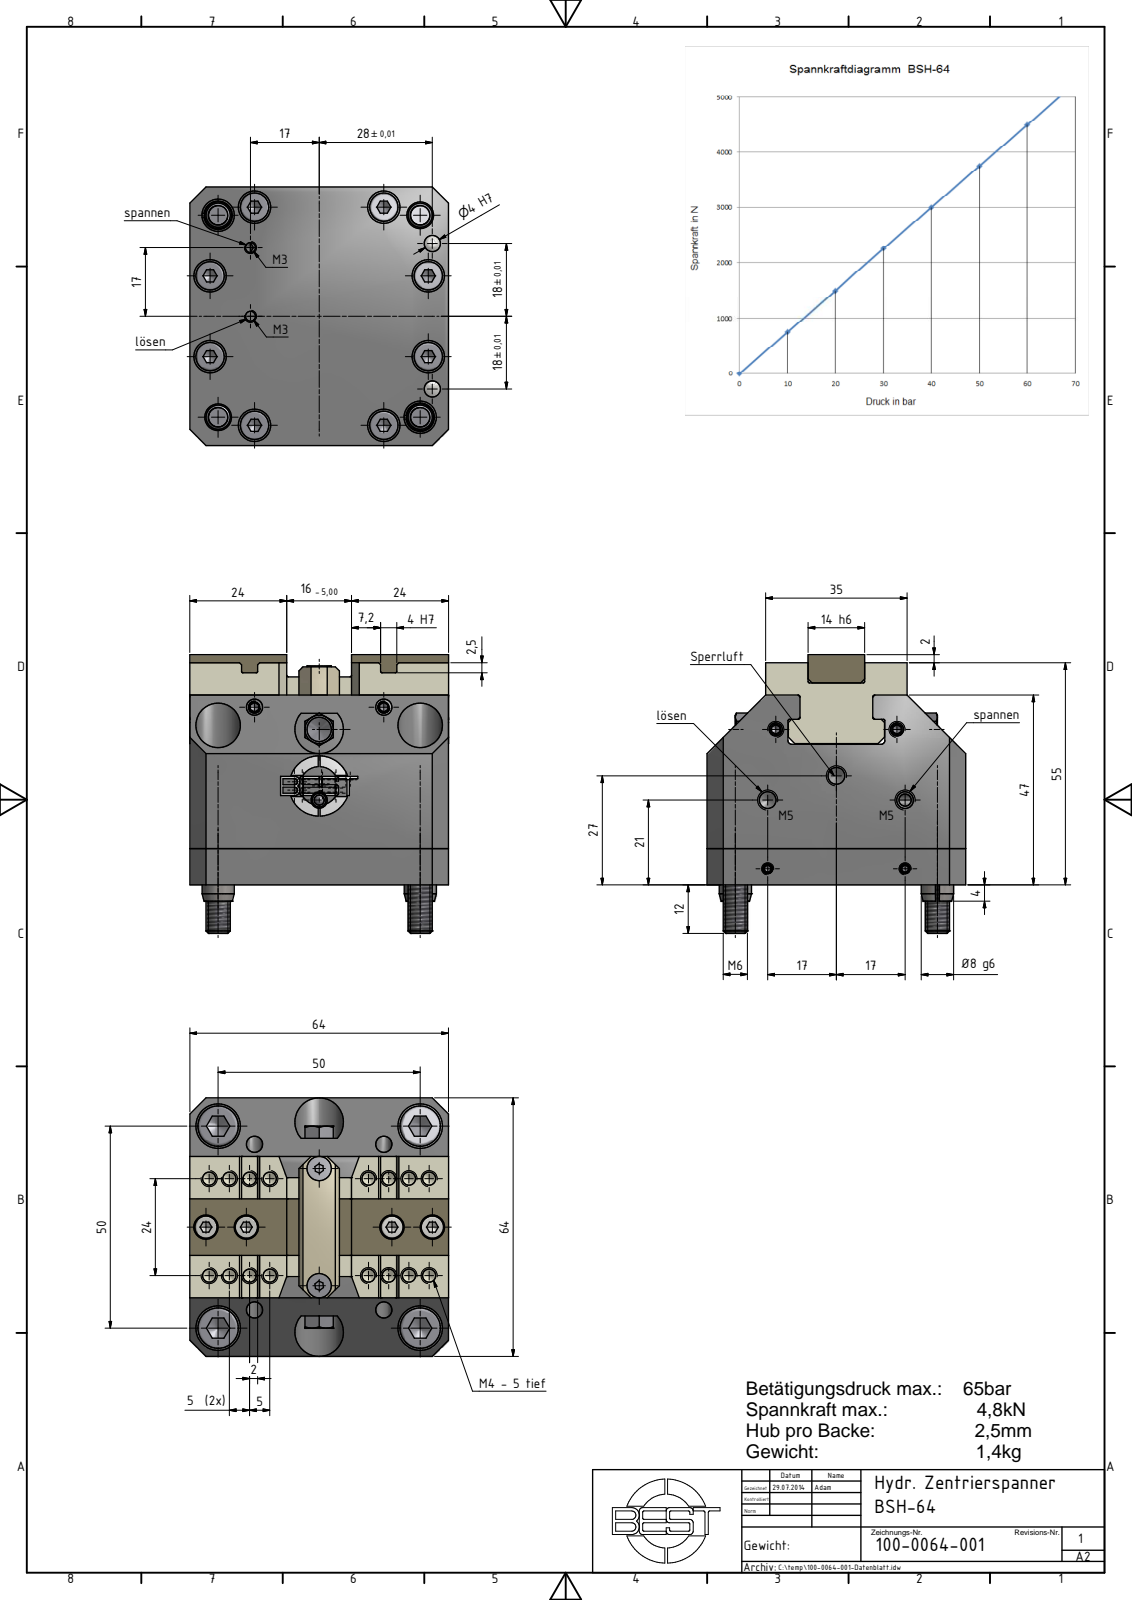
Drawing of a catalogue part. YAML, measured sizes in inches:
part_name: "100-0064-001-Kd"
step_written_by: "Autodesk Inventor 2013 (AUTOMOTIVE_DESIGN)"
units: inches
bodies: {solids: 1, faces: 504, planar: 326, cylindrical: 123, other: 55}
overall_size: [2.717, 2.521, 2.52]
volume: 11.51
surface_area: 56.76
round_holes:
  - {diameter: 0.128, count: 16}
  - {diameter: 0.26, count: 4}
  - {diameter: 0.433, count: 4}
  - {diameter: 0.163, count: 3}
  - {diameter: 0.097, count: 2}
  - {diameter: 0.157, count: 2}
  - {diameter: 0.315, count: 2}
  - {diameter: 0.194, count: 1}
round_bosses_or_shafts:
  - {diameter: 0.394, count: 4}
  - {diameter: 0.236, count: 4}
partial_cylinders:
  - {radius: 0.009, count: 18}
  - {radius: 0.024, count: 12}
  - {radius: 0.016, count: 4}
  - {radius: 0.03, count: 4}
  - {radius: 0.053, count: 4}
  - {radius: 0.188, count: 1}
  - {radius: 0.236, count: 1}
  - {radius: 0.294, count: 1}
face_to_face_distances: [2.52, 0.787, 1.378, 1.37, 2.52, 0.217, 1.728, 1.732, 0.079, 0.571]
hole_center_spacings: [0.197, 0.965, 0.394, 0.945, 1.024, 1.553, 1.818, 1.356]
